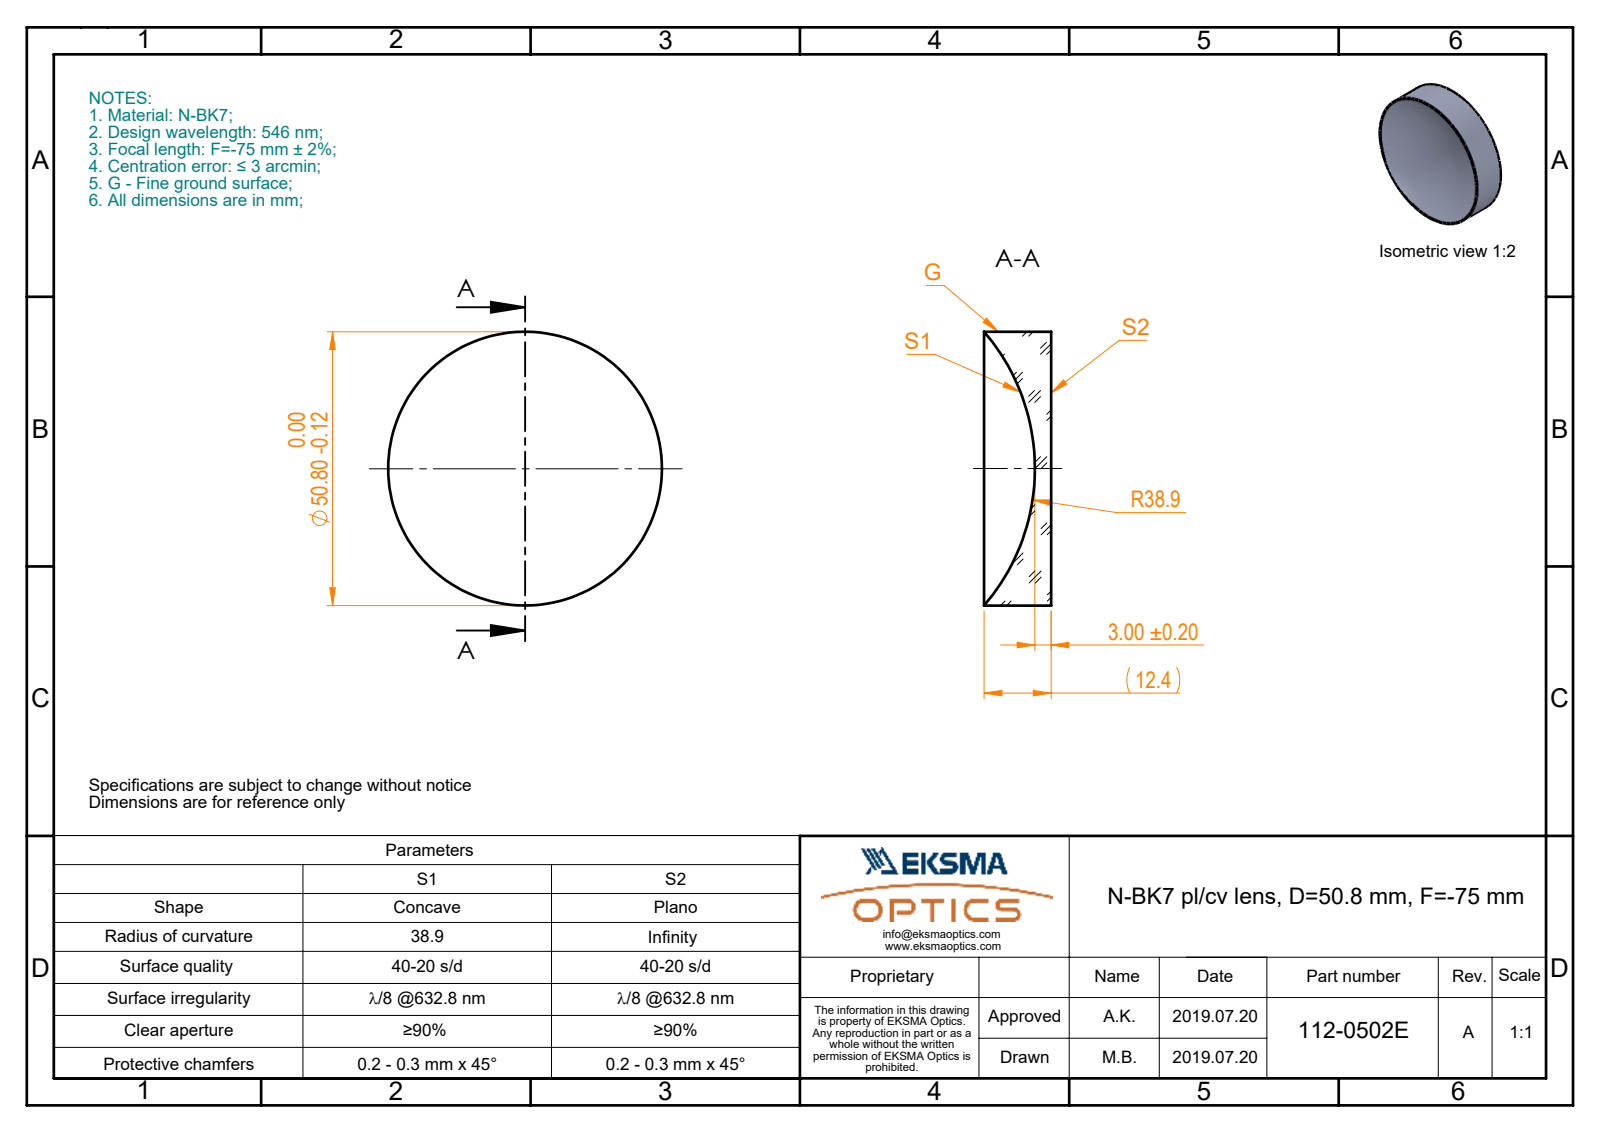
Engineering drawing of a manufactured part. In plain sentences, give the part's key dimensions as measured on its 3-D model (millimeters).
The part is named "112-0502 BK7 pl-cv 50.8 F-75". Its 3-D file was written by "SolidWorks 2017 (CONFIG_CONTROL_DESIGN)". It is 1 solid with 5 faces: 1 planar, 2 cylindrical and 2 other. Overall it measures 50.8 by 50.8 by 12.44 millimeters. Its volume is 15 204 cubic millimeters and its surface area 6 318 square millimeters. Round bosses or shafts: 1 of diameter 50.8.
